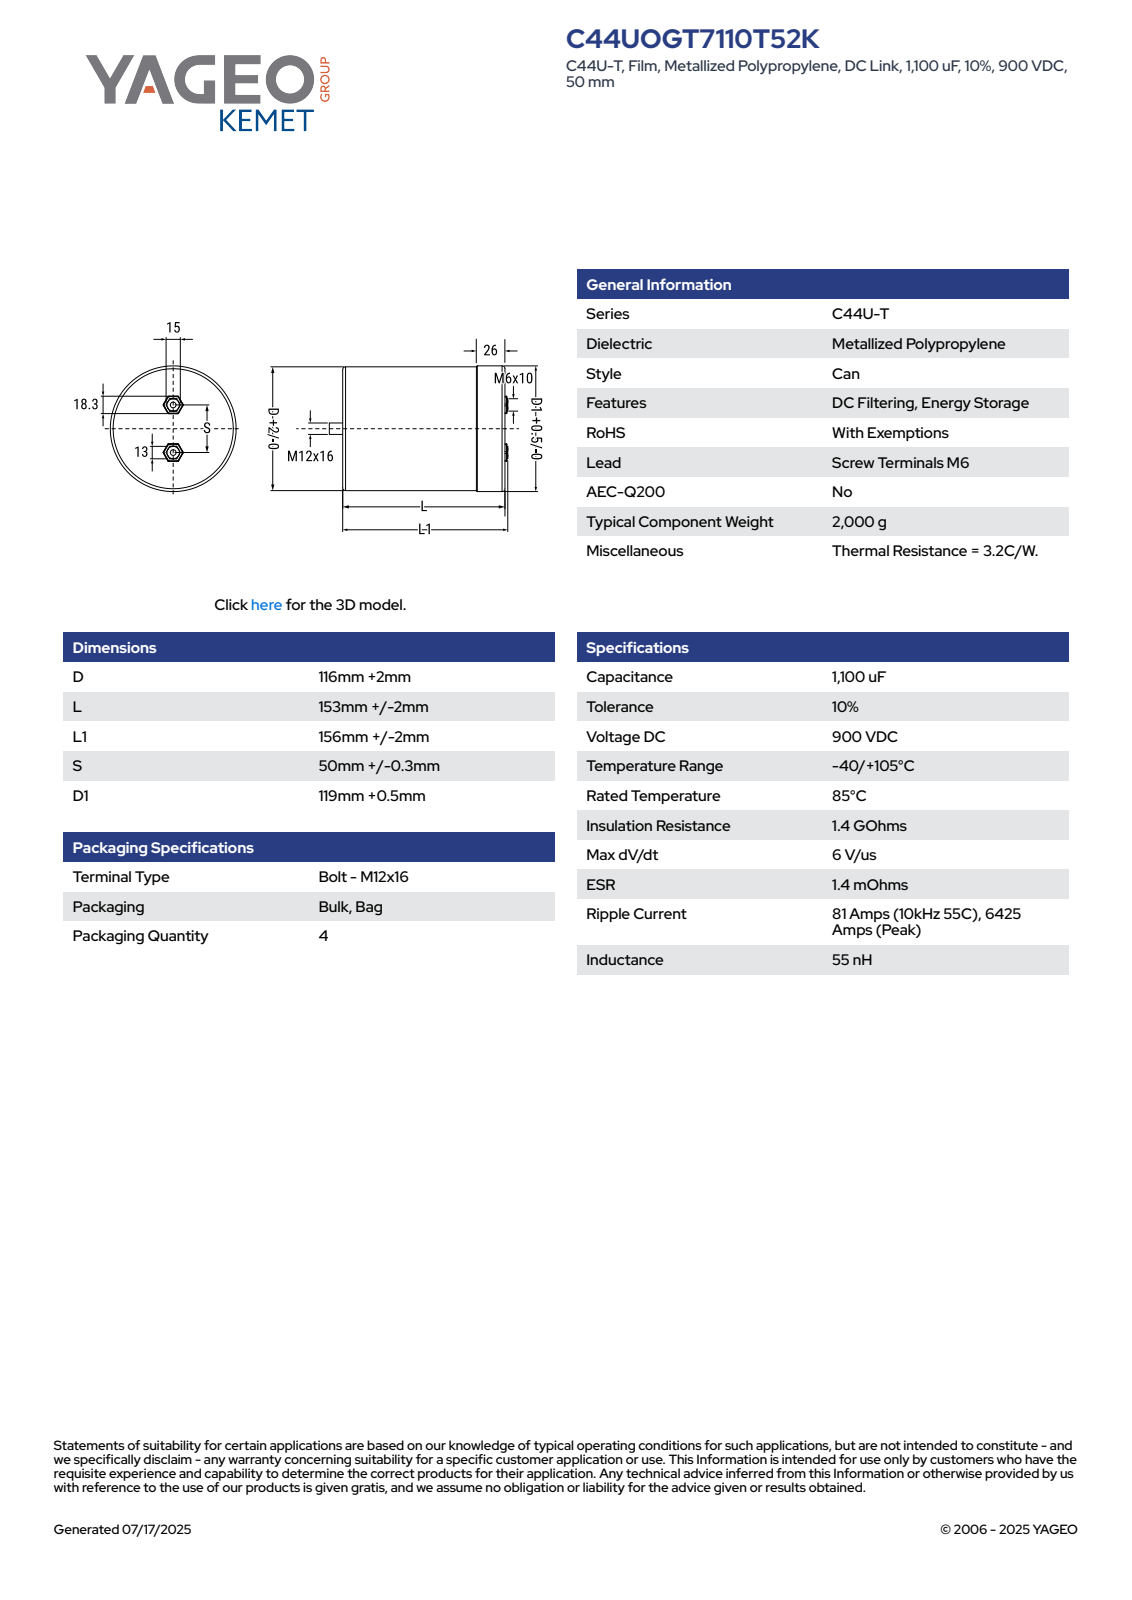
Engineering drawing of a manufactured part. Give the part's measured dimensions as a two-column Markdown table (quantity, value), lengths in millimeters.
| quantity | value |
| --- | --- |
| part name | CFP_C44UMH_116X153_D118L155S50L1158D1119.5 |
| STEP written by | SolidWorks 2014 (AUTOMOTIVE_DESIGN) |
| units | millimeters |
| bodies | 1 solid, 92 faces (44 planar, 17 cylindrical, 31 other) |
| overall size | 174 × 119.5 × 119.5 |
| volume | 1 705 000 mm³ |
| surface area | 81 335 mm² |
| round holes (diameter × count) | 6 × 2 |
| round bosses / shafts (diameter × count) | 13 × 2, 119.5 × 1, 118 × 1, 12 × 1 |
| partial cylindrical surfaces (radius × count) | 59.01 × 1 |
| main face-to-face distances | 155, 157, 2, 129, 26, 28, 158, 29, 3, 1 |
| hole center spacings | 50 |
